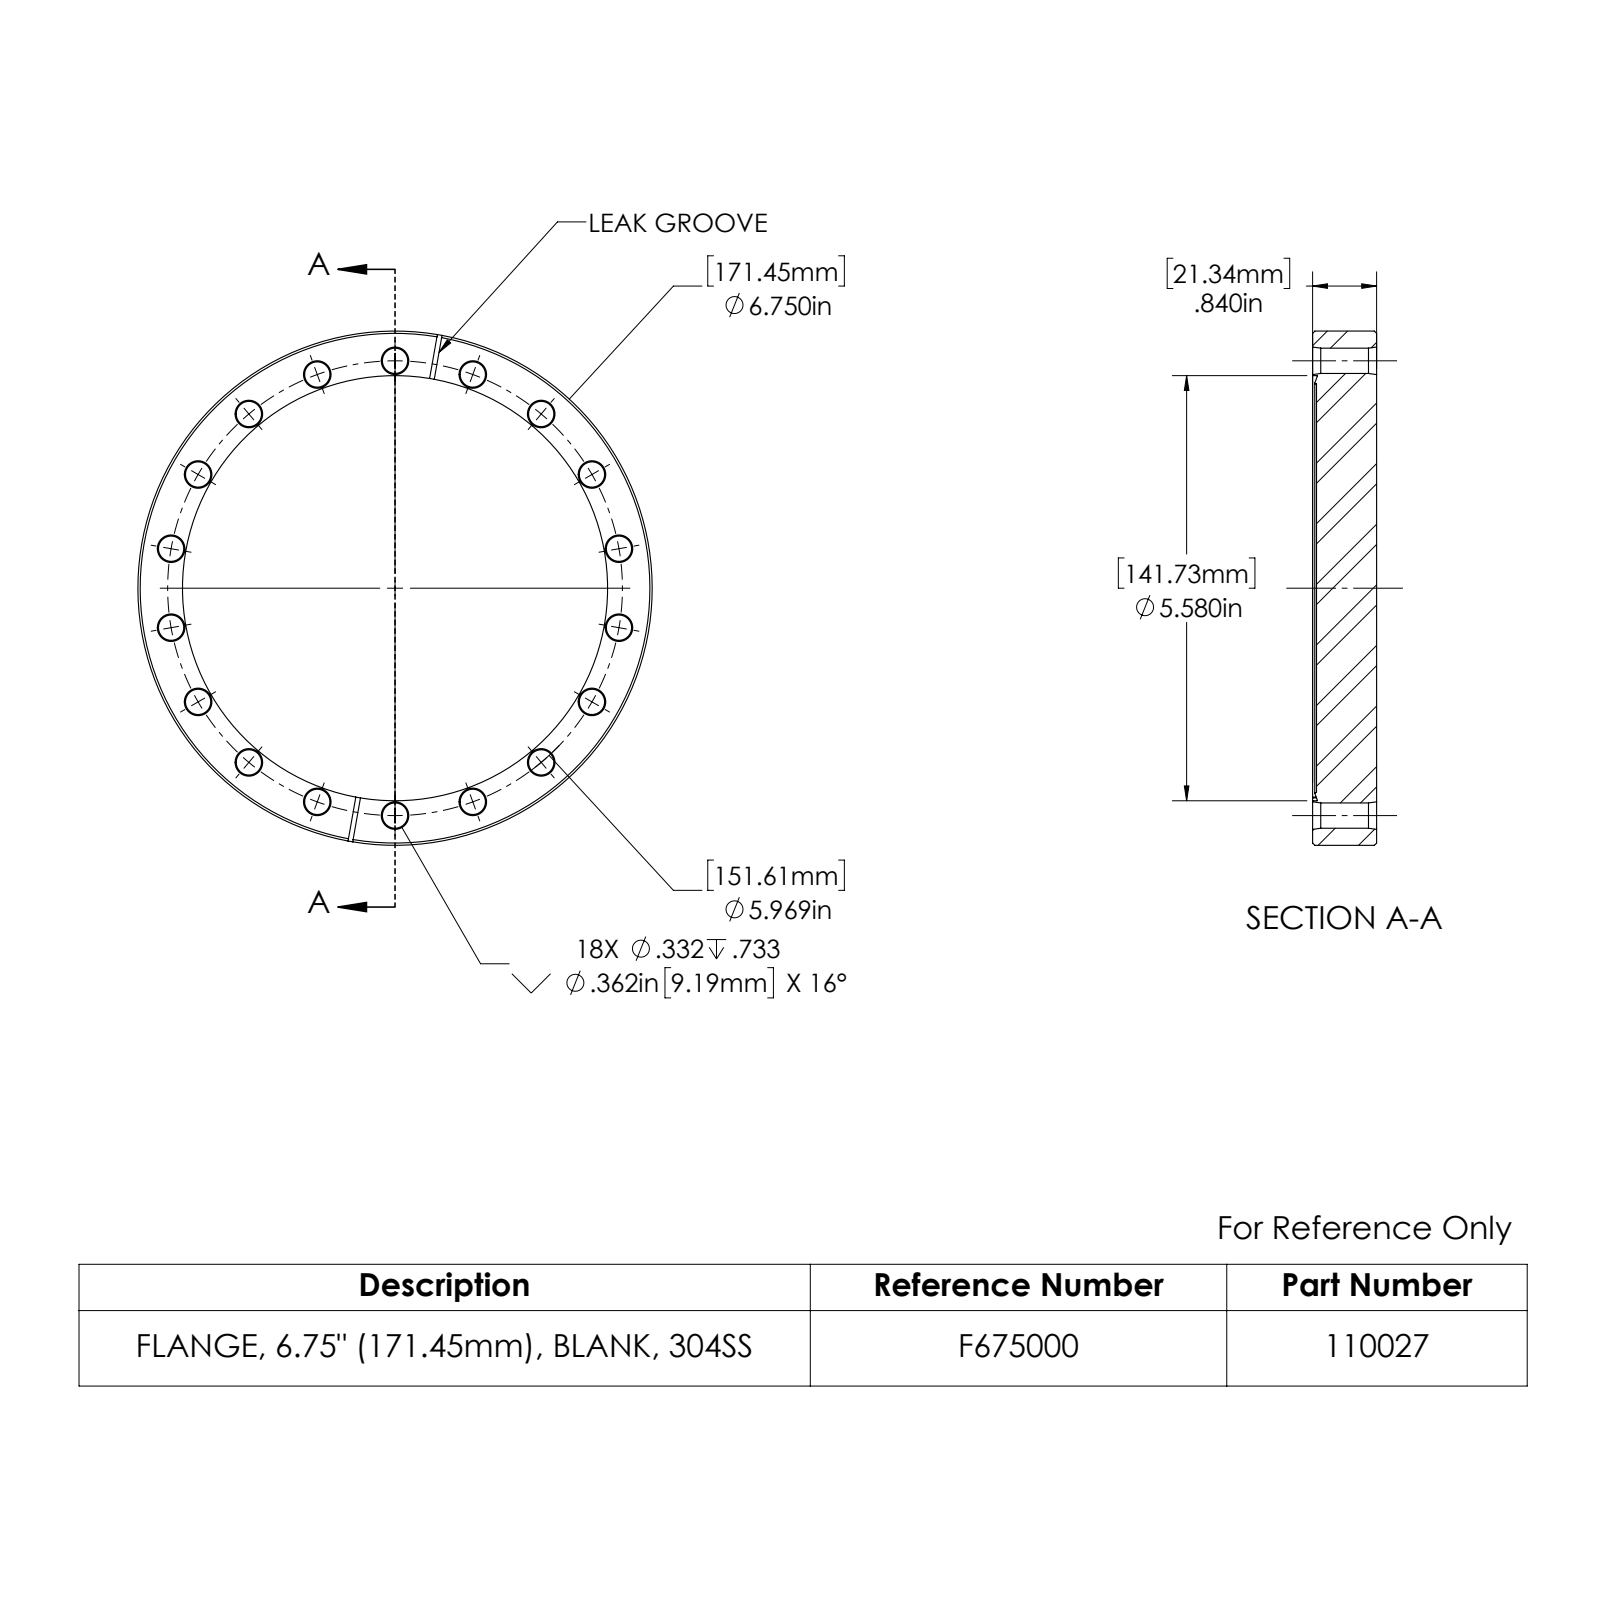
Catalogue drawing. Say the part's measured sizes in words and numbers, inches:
The part is named "110027". Its 3-D file was written by "SolidWorks 2022 (AUTOMOTIVE_DESIGN)". It is 1 solid with 137 faces: 10 planar, 40 cylindrical and 87 other. Overall it measures 6.75 by 6.75 by 0.84 inches. Its volume is 27.46 cubic inches and its surface area 102.5 square inches. Round holes: 18 of diameter 0.332, 1 of diameter 5.58. Round bosses or shafts: 1 of diameter 6.75. The main face-to-face distances are 0.789, 0.051, 0.84, 0.052, 0.788, 0.06, 0.062, 0.064, 0.062. The hole center spacings are 2.984, 1.037, 2.985, 4.572, 2.041, 5.878, 3.837, 5.169.
